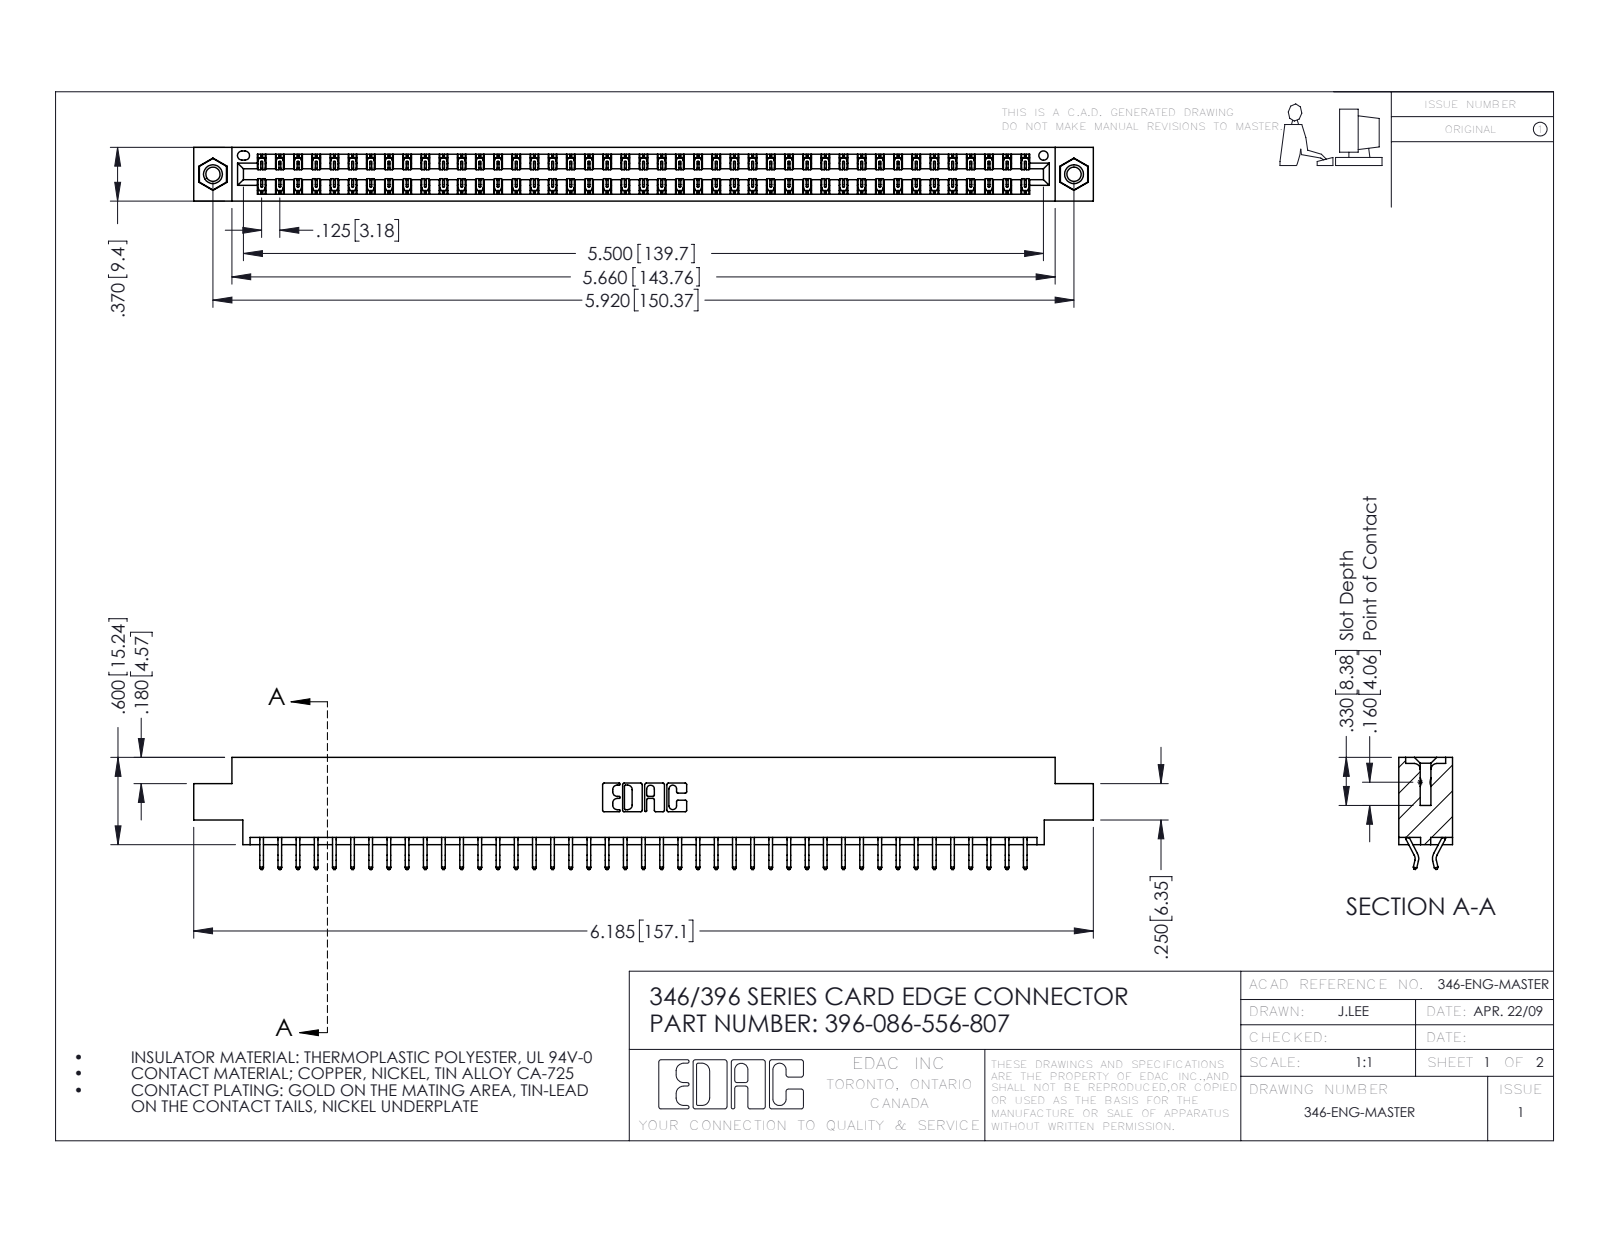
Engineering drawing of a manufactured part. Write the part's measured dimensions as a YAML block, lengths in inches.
part_name: "345-292-001_556 Tail; 345-250-001_345-250-005-103; 346 Part_0.170 Offset - 0.156 Dia-TI; 396-086-556-807"
step_written_by: "SolidWorks 2016 (CONFIG_CONTROL_DESIGN)"
units: inches
bodies: {solids: 89, faces: 5174, planar: 3466, cylindrical: 1692, other: 16}
overall_size: [6.185, 0.77, 0.37]
volume: 0.925
surface_area: 32.52
round_holes:
  - {diameter: 0.098, count: 2}
  - {diameter: 0.125, count: 2}
  - {diameter: 0.156, count: 2}
  - {diameter: 0.064, count: 1}
round_bosses_or_shafts:
  - {diameter: 0.155, count: 2}
partial_cylinders:
  - {radius: 0.006, count: 129}
  - {radius: 0.01, count: 22}
  - {radius: 0.007, count: 6}
  - {radius: 0.031, count: 6}
  - {radius: 0.026, count: 3}
  - {radius: 0.01, count: 2}
  - {radius: 0.014, count: 2}
  - {radius: 0.022, count: 2}
face_to_face_distances: [0.048, 0.322, 0.37, 0.25, 0.025, 0.072, 0.298, 0.275, 0.222, 0.148]
hole_center_spacings: [0.246, 5.711, 5.92]
